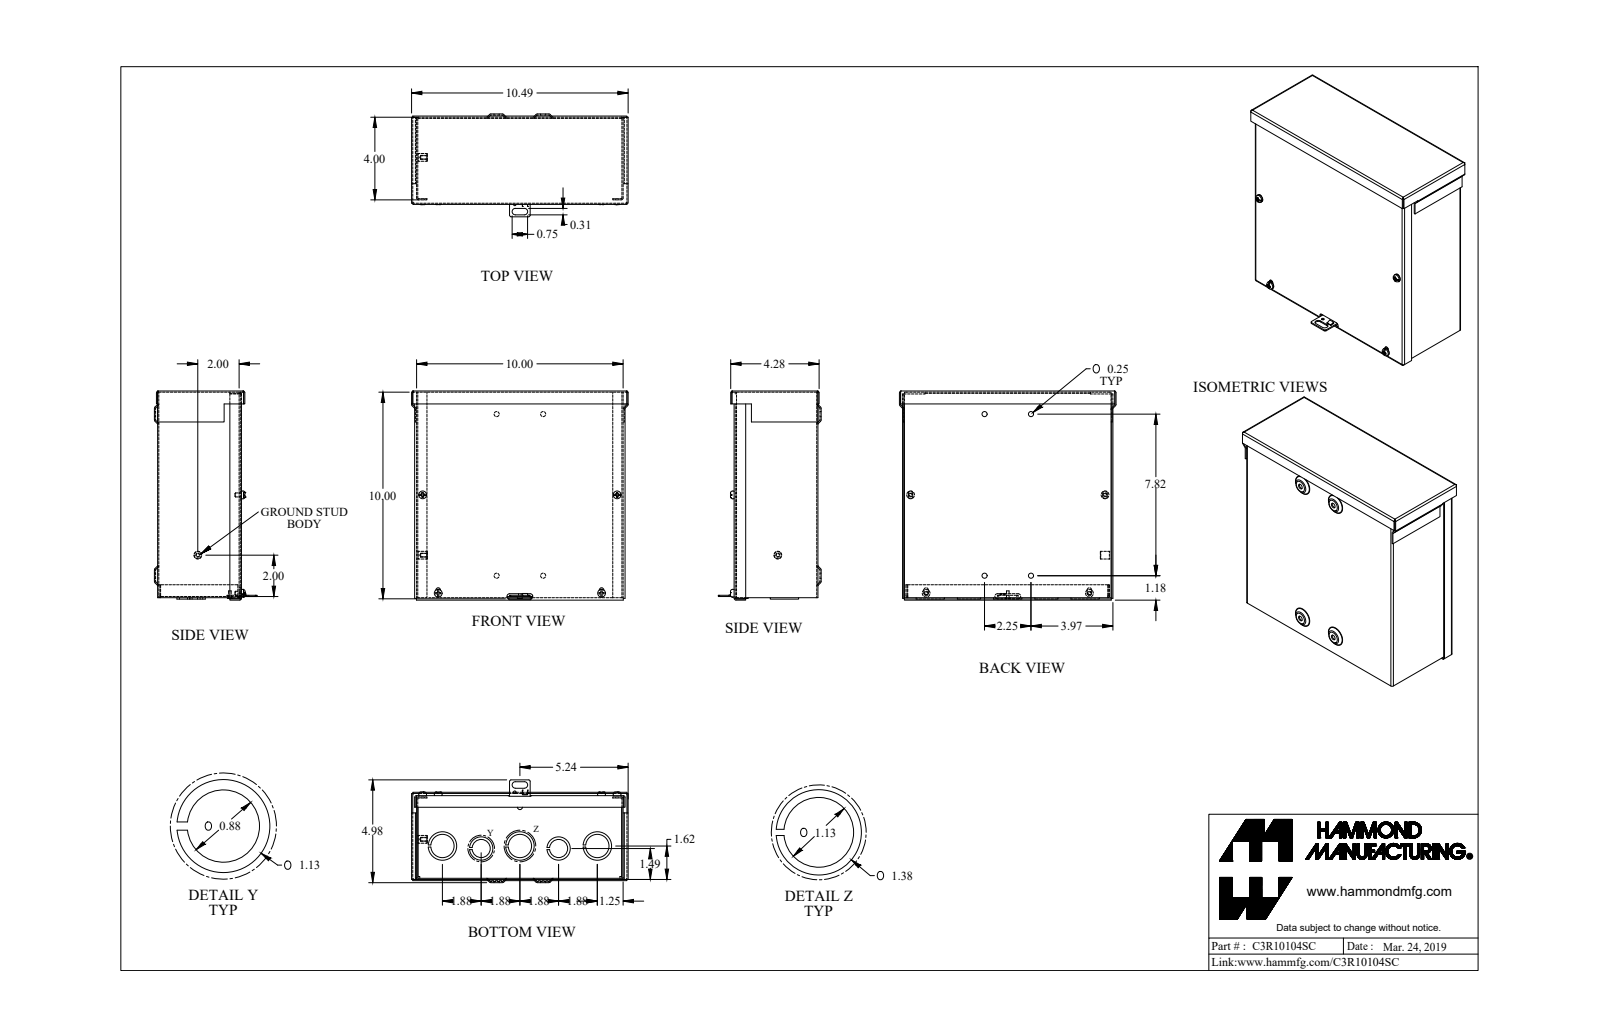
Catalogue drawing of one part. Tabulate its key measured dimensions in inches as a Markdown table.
| quantity | value |
| --- | --- |
| part name | C3R10104SC_Default |
| STEP written by | SolidWorks 2019 (CONFIG_CONTROL_DESIGN) |
| units | inches |
| bodies | 11 solids, 429 faces (226 planar, 117 cylindrical, 86 other) |
| overall size | 10.489 × 10.12 × 4.977 |
| volume | 24.53 in³ |
| surface area | 867.4 in² |
| round holes (diameter × count) | 0.17 × 4, 0.25 × 4, 1.125 × 3, 0.875 × 2, 0.125 × 1, 0.137 × 1, 0.156 × 1 |
| round bosses / shafts (diameter × count) | 0.375 × 4, 0.19 × 4, 1.375 × 2, 1.125 × 2, 1.375 × 1, 0.375 × 1, 0.125 × 1 |
| partial cylindrical surfaces (radius × count) | 0.029 × 21, 0.086 × 21, 0.109 × 8, 0.125 × 8, 0.156 × 2 |
| main face-to-face distances | 0.057, 4, 3.943, 9.943, 4.057, 10, 0.057, 9.886, 9.886, 9.943 |
| hole center spacings | 5.302, 7.021, 3.75, 1.879, 1.88, 2.25, 2.946, 4.195 |
